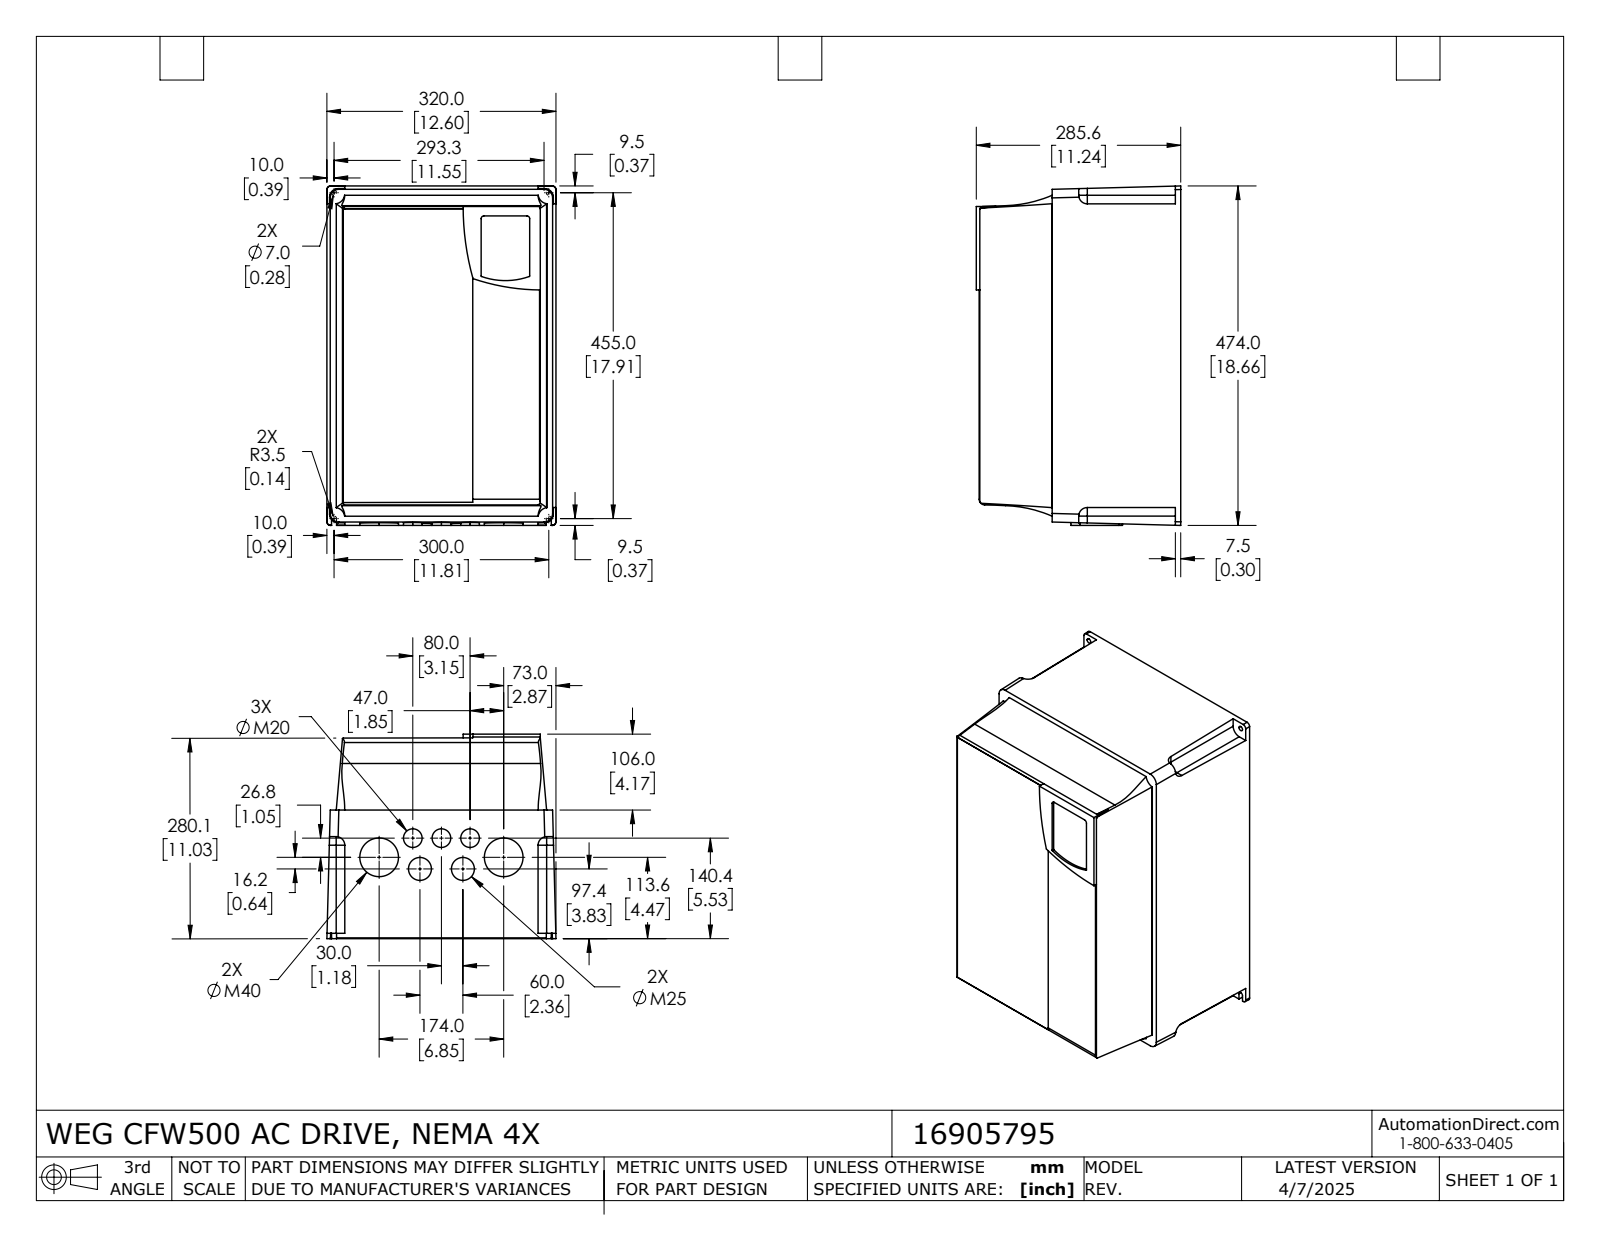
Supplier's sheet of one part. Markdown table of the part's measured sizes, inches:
| quantity | value |
| --- | --- |
| part name | 16905795 |
| STEP written by | SolidWorks 2021 (AUTOMOTIVE_DESIGN) |
| units | inches |
| bodies | 1 solid, 121 faces (56 planar, 57 cylindrical, 8 other) |
| overall size | 18.661 × 12.598 × 11.244 |
| volume | 2 356 in³ |
| surface area | 1 100 in² |
| round holes (diameter × count) | 0.276 × 2 |
| round bosses / shafts (diameter × count) | 1.026 × 3, 2.128 × 2, 1.262 × 2 |
| partial cylindrical surfaces (radius × count) | 0.472 × 12, 0.197 × 4, 0.033 × 2, 0.039 × 2, 0.138 × 2, 0.152 × 2, 0.02 × 1, 0.116 × 1 |
| main face-to-face distances | 11.087, 7.071, 4.016, 11.126, 4.055, 0.039, 0.118, 11.244, 4.173, 0.157 |
| hole center spacings | 11.811 |
